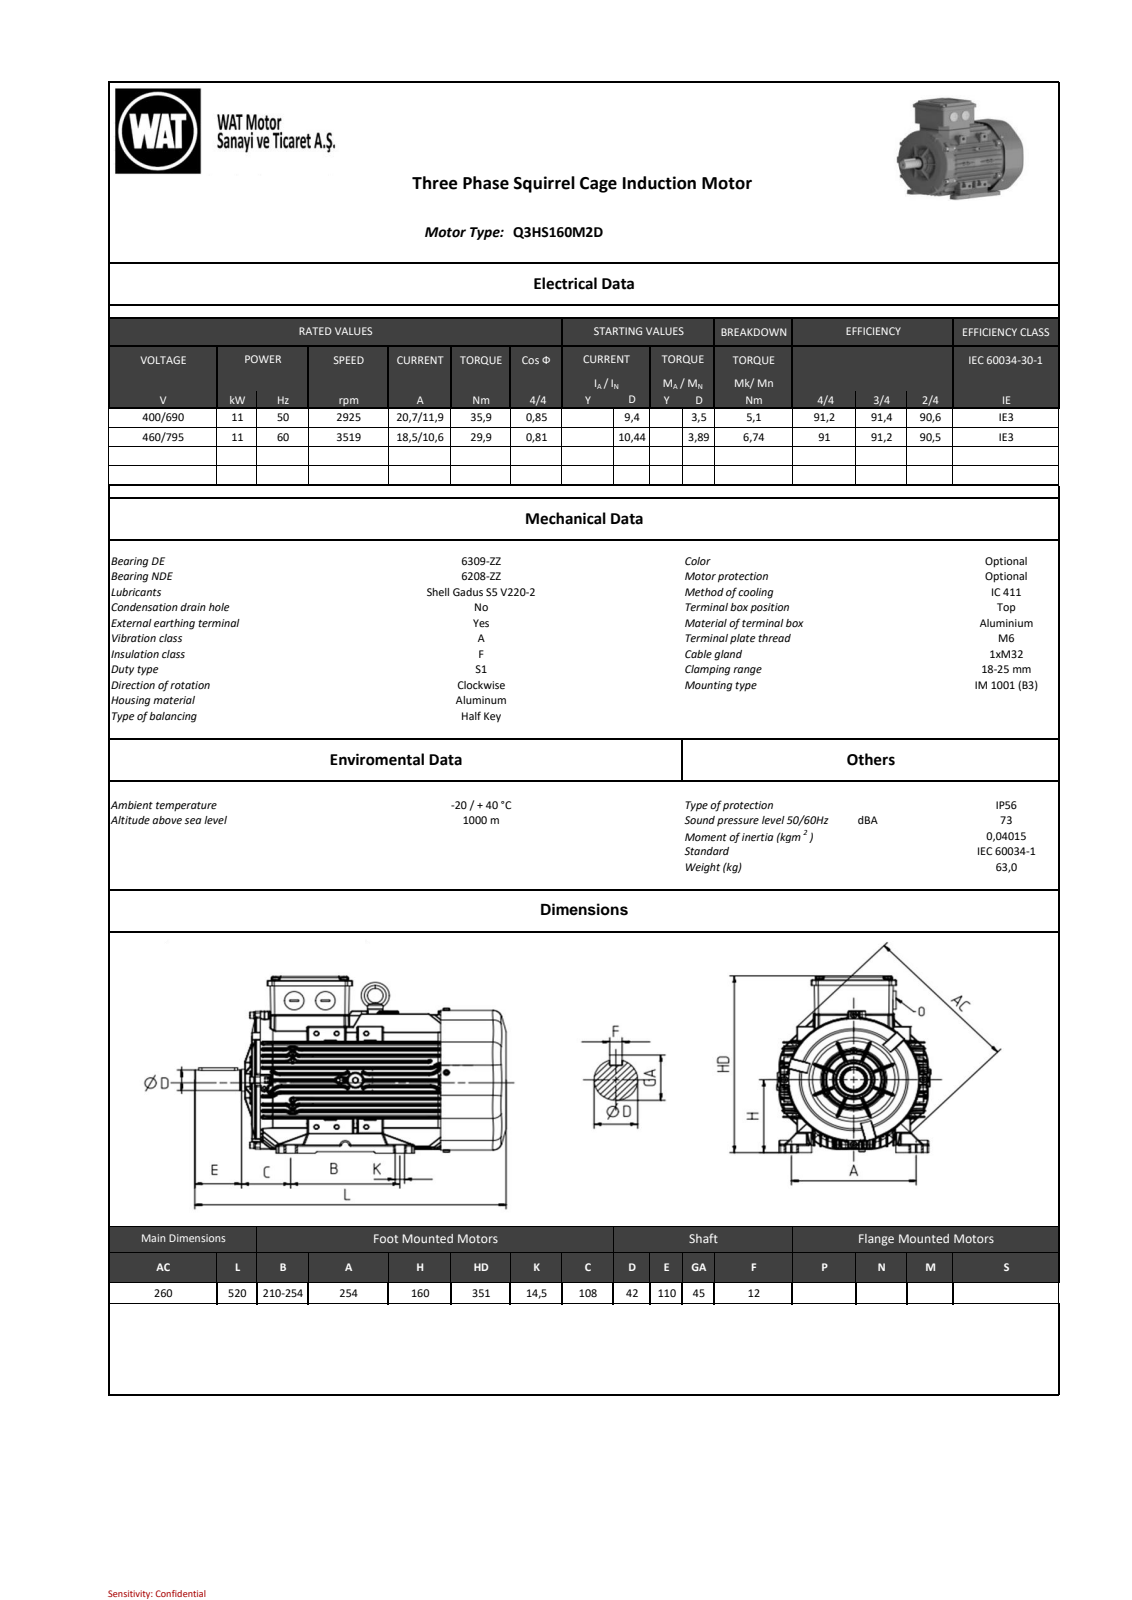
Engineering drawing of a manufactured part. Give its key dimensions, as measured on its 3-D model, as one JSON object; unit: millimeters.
{"part_name": "QHS series_ 160_B3_stp_objects", "step_written_by": "SIEMENS PLM Software NX2206.8101 (AP203_CONFIGURATION_CONTROLLED_3D_DESIGN_OF_MECHANICAL_PARTS_AND_ASSEMBLIES_MIM_LF)", "units": "millimeters", "bodies": {"solids": 0, "faces": 7565, "planar": 1768, "cylindrical": 3210, "other": 2587}, "overall_size": [519.49, 362.95, 287.5], "round_holes": [[5.5, 3], [8.48, 2], [8.48, 1], [16, 1], [17, 1], [68.67, 1], [82, 1], [180, 1]], "round_bosses_or_shafts": [[13, 4], [8, 3], [38, 2], [230.5, 1], [86.77, 1], [45, 1], [42, 1], [41.4, 1]], "partial_cylinders_radius": [[0.8, 845], [1, 775], [2, 261], [3, 85], [0.5, 69], [5, 36], [60, 16], [10, 12]], "face_to_face_distances": [1.5, 10.42, 10.56, 10.28, 20.84, 125.58, 94.46, 4, 104.9, 115.18], "hole_center_spacings": [74.95, 106, 143, 149.91, 178.91, 217.51]}
